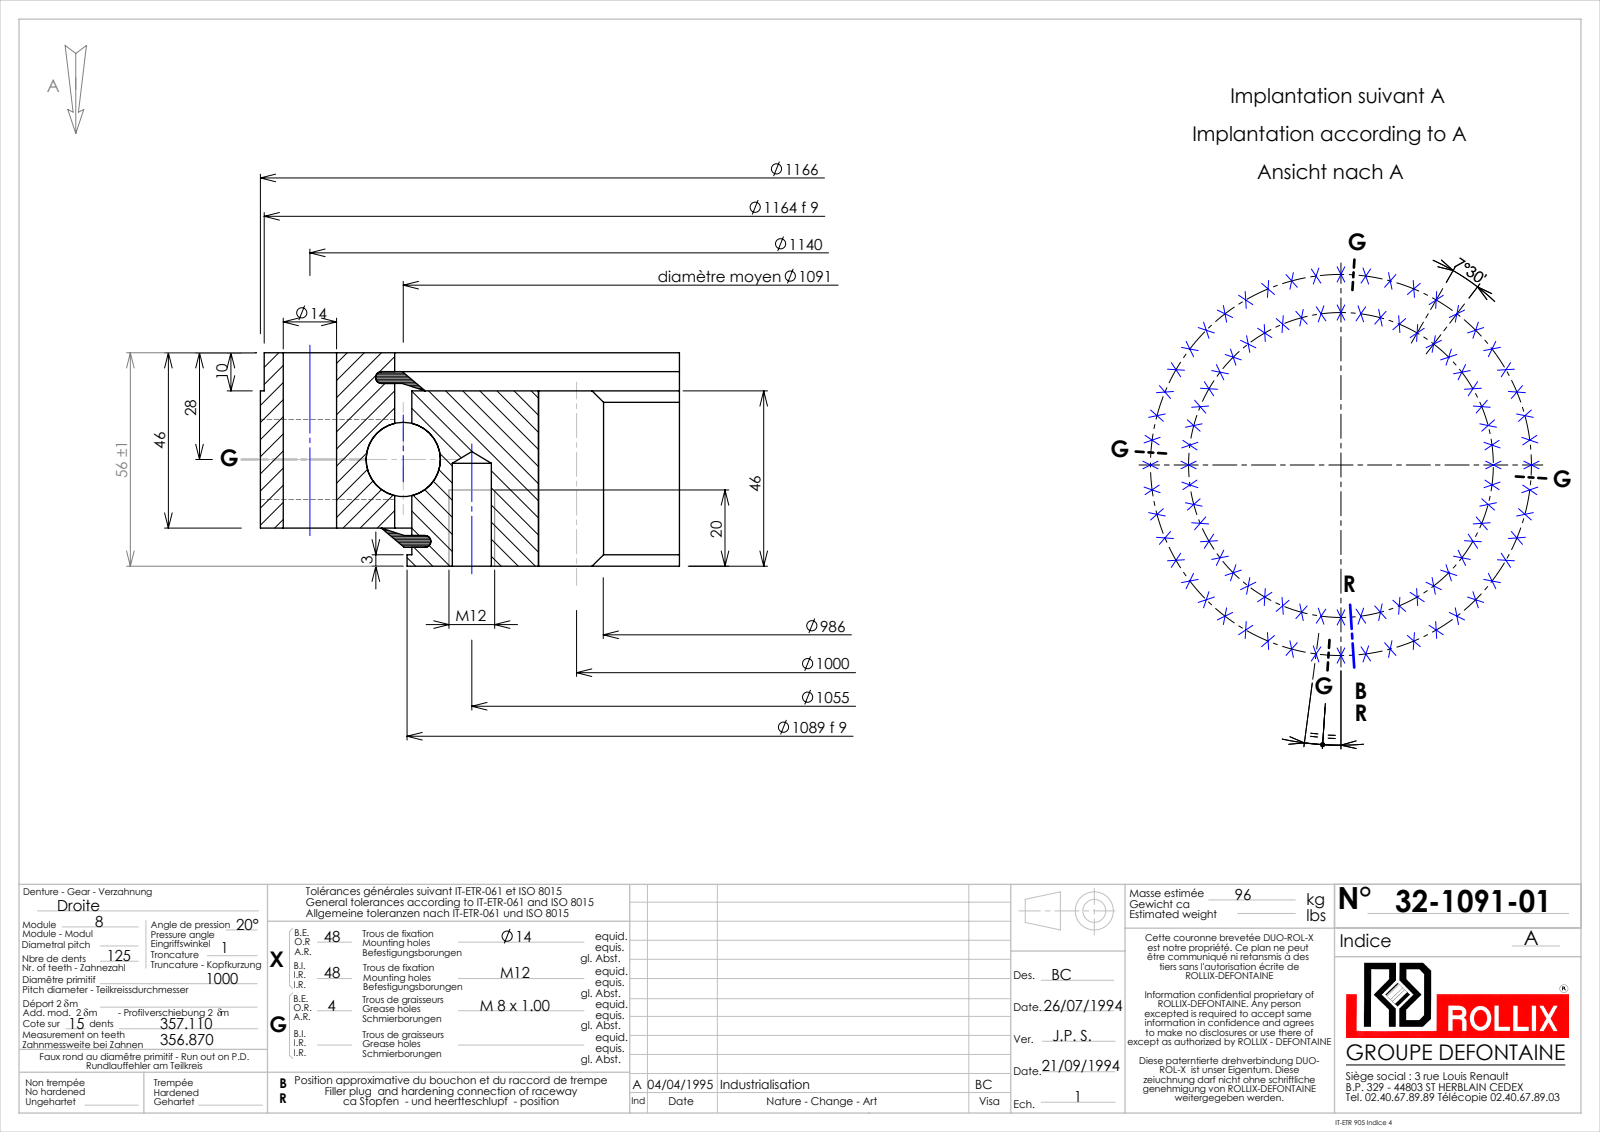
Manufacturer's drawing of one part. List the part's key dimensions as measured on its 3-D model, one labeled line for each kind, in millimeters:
Part name (STEP PRODUCT): 32-1091-01
STEP written by: SolidWorks 2016 (CONFIG_CONTROL_DESIGN)
Units: millimetres
Bodies: 9 solids, 1196 faces (304 planar, 477 cylindrical, 415 other)
Overall size (bounding box): 1183.07 × 1183.07 × 56
Volume: 11 060 000 mm³ · Surface area: 1 739 000 mm²
Round holes (diameter × count): ⌀10.25 ×48, ⌀14 ×48, ⌀7 ×4, ⌀1095.5 ×1
Round bosses / shafts (diameter × count): ⌀8 ×4, ⌀1166 ×1, ⌀1164 ×1, ⌀1089 ×1, ⌀1086.5 ×1
Partial cylindrical surfaces — rounded edges, fillets, slot ends (radius × count): R493 ×1, R510 ×1
Main face-to-face distances: 46, 10, 36, 56, 1.95, 5.05, 43, 8.05, 47.95, 37.95
Hole centre spacings: 205.82, 69, 403.73, 527.5, 339.12, 586.13, 746, 137.7
